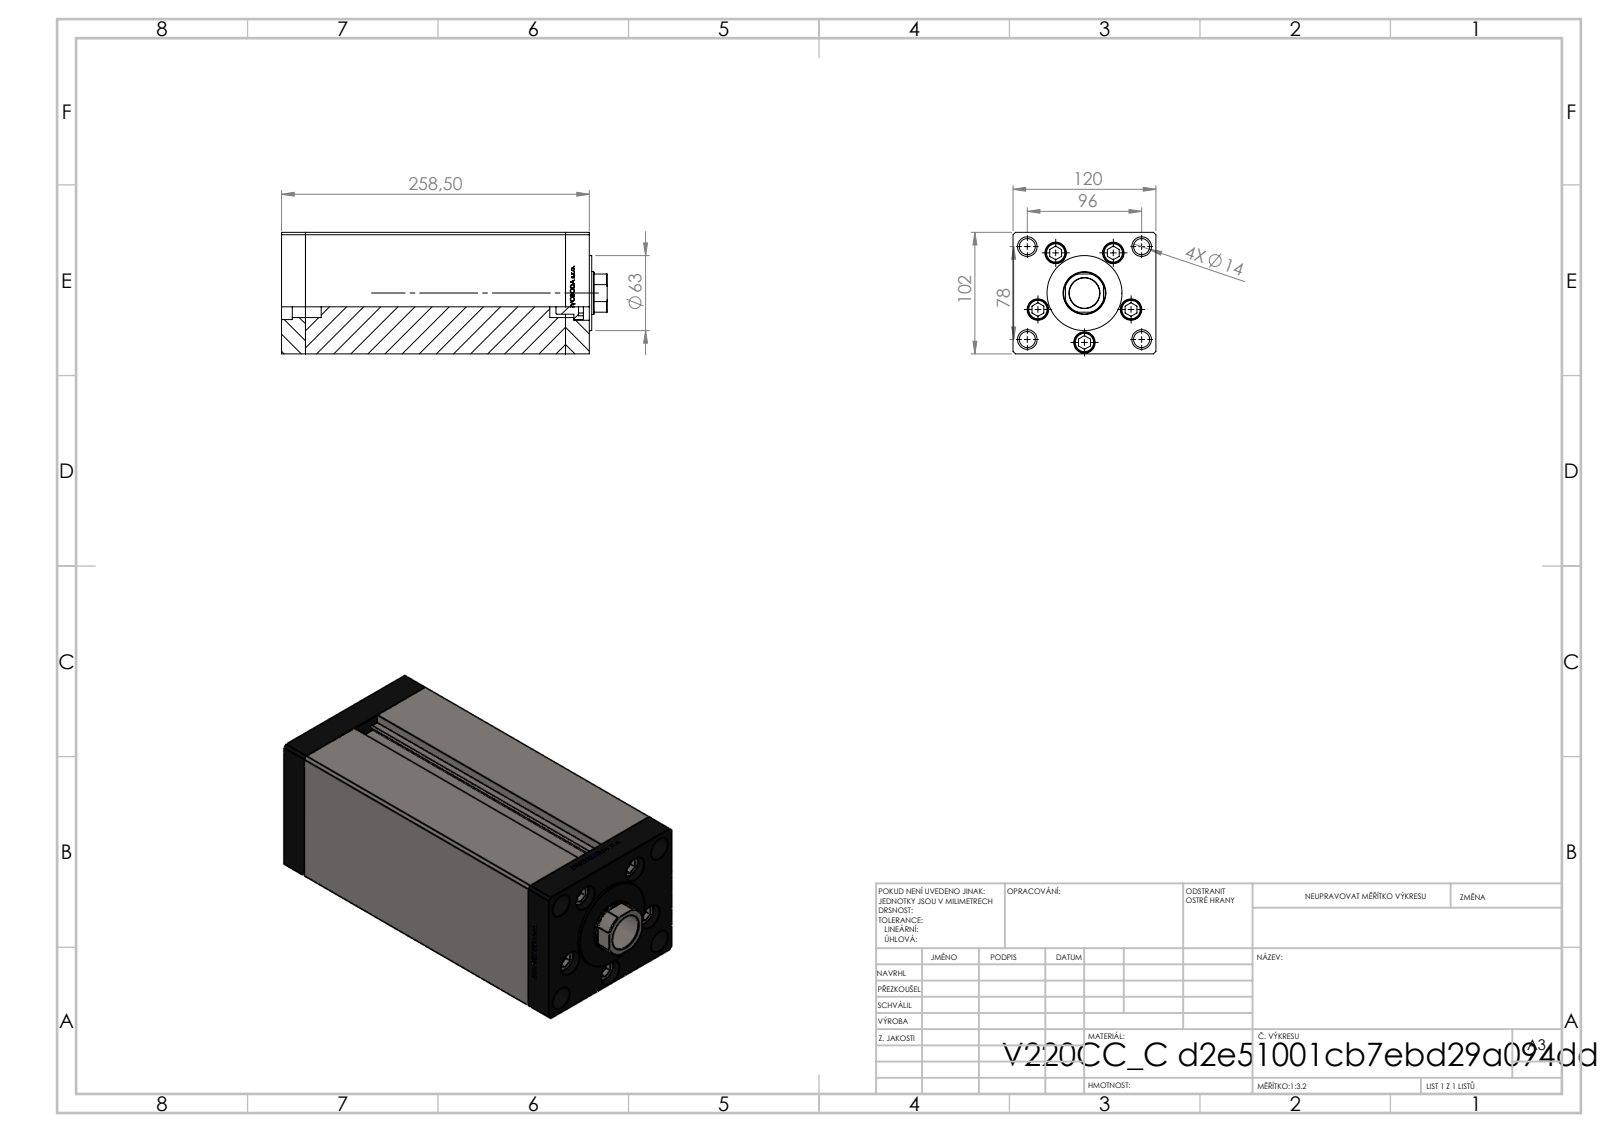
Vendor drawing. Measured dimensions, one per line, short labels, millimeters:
name: ALLEN BOLT; V220C FRONT; V220C BACK_C; V220C_VC_C (+1 more)
written by: SolidWorks 2019 (CONFIG_CONTROL_DESIGN)
unit: mm
bodies: 13 solids, 1165 faces (542 planar, 161 cylindrical, 462 other)
size: 273.5 × 120 × 102
volume: 2 638 000 mm³; area: 337 176 mm²
holes: 9× ⌀13.5, 5× ⌀18, 4× ⌀12, 4× ⌀16.5, 1× ⌀17, 1× ⌀25.5, 1× ⌀36
bosses: 5× ⌀8, 4× ⌀17, 1× ⌀63
rounds: 2× R0.93, 1× R17.5
face distances: 120, 102, 20, 218.5, 238.5, 34.25, 258.5, 224.25, 204.25, 14.25
hole spacings: 41.5, 61.85, 24.39, 26.69, 47.92, 48.07, 49.84, 53.57
